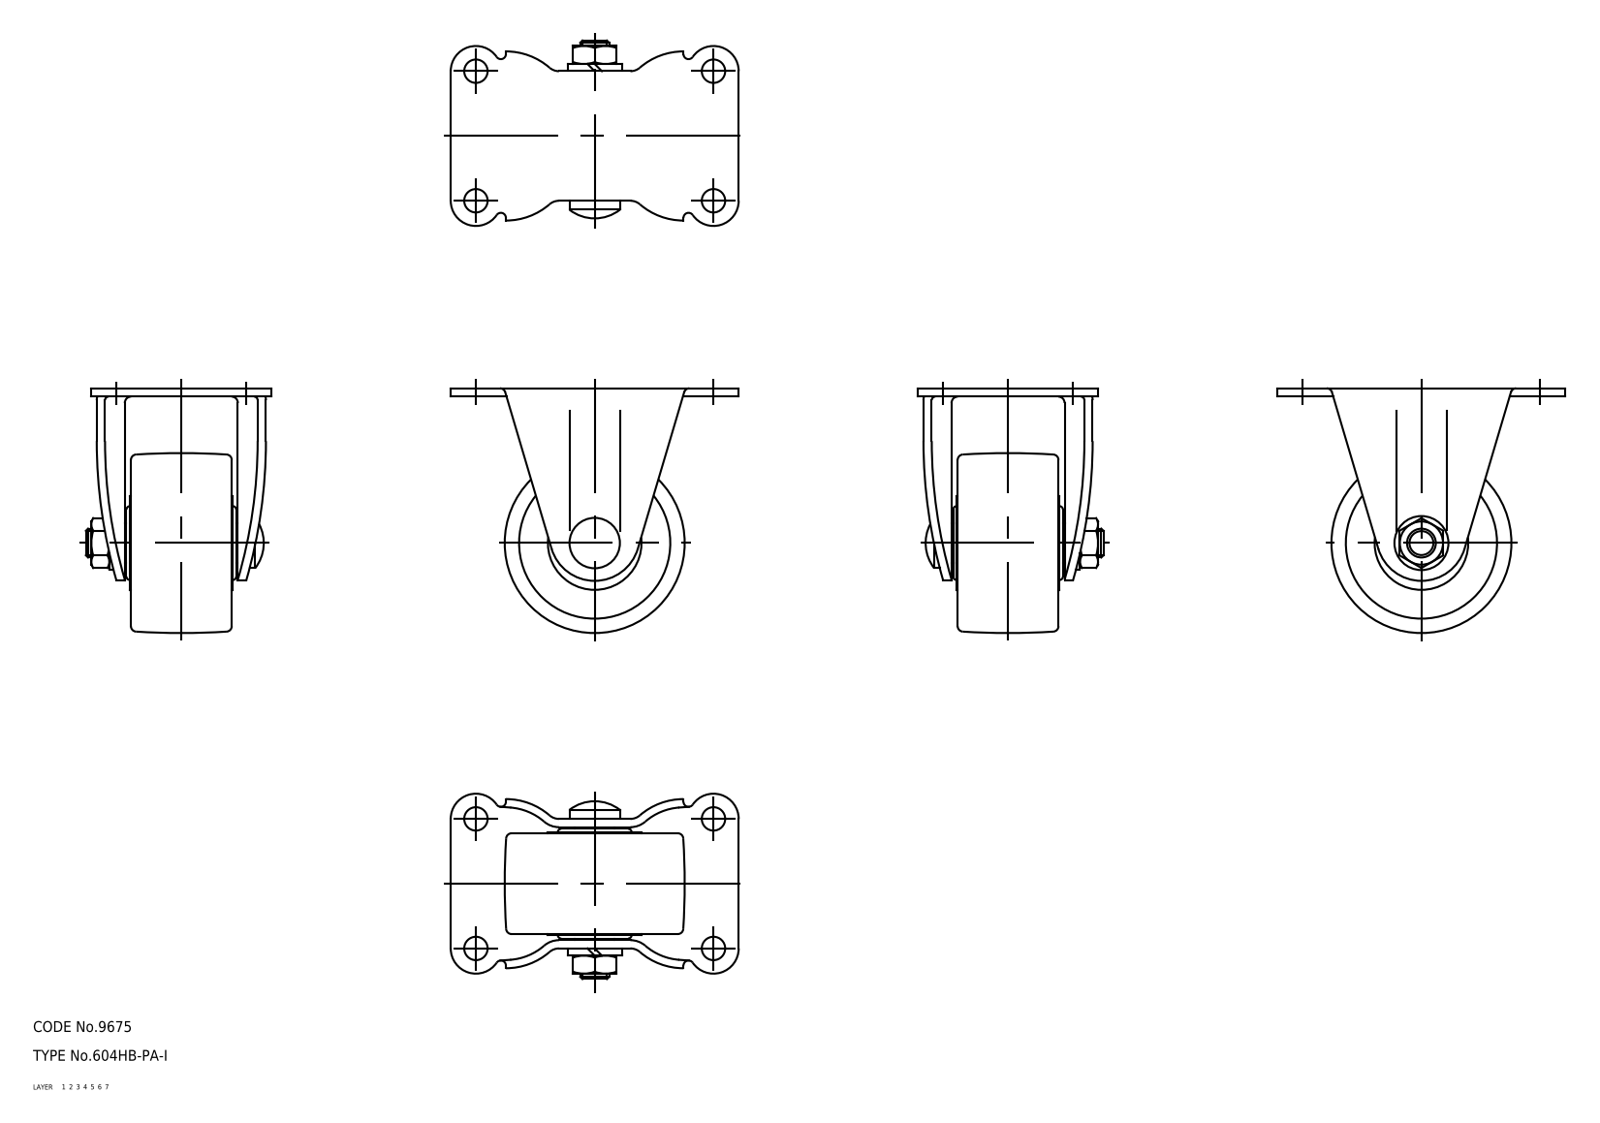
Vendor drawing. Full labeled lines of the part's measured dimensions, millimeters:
Part name (STEP PRODUCT): 67119697; 67119710; 67119723
STEP written by: CADfix (AUTOMOTIVE_DESIGN)
Units: millimetres
Bodies: 3 solids, 162 faces (0 planar, 0 cylindrical, 162 other)
Overall size (bounding box): 80 × 68 × 51.5
Volume: 72 003 mm³ · Surface area: 25 395 mm²
